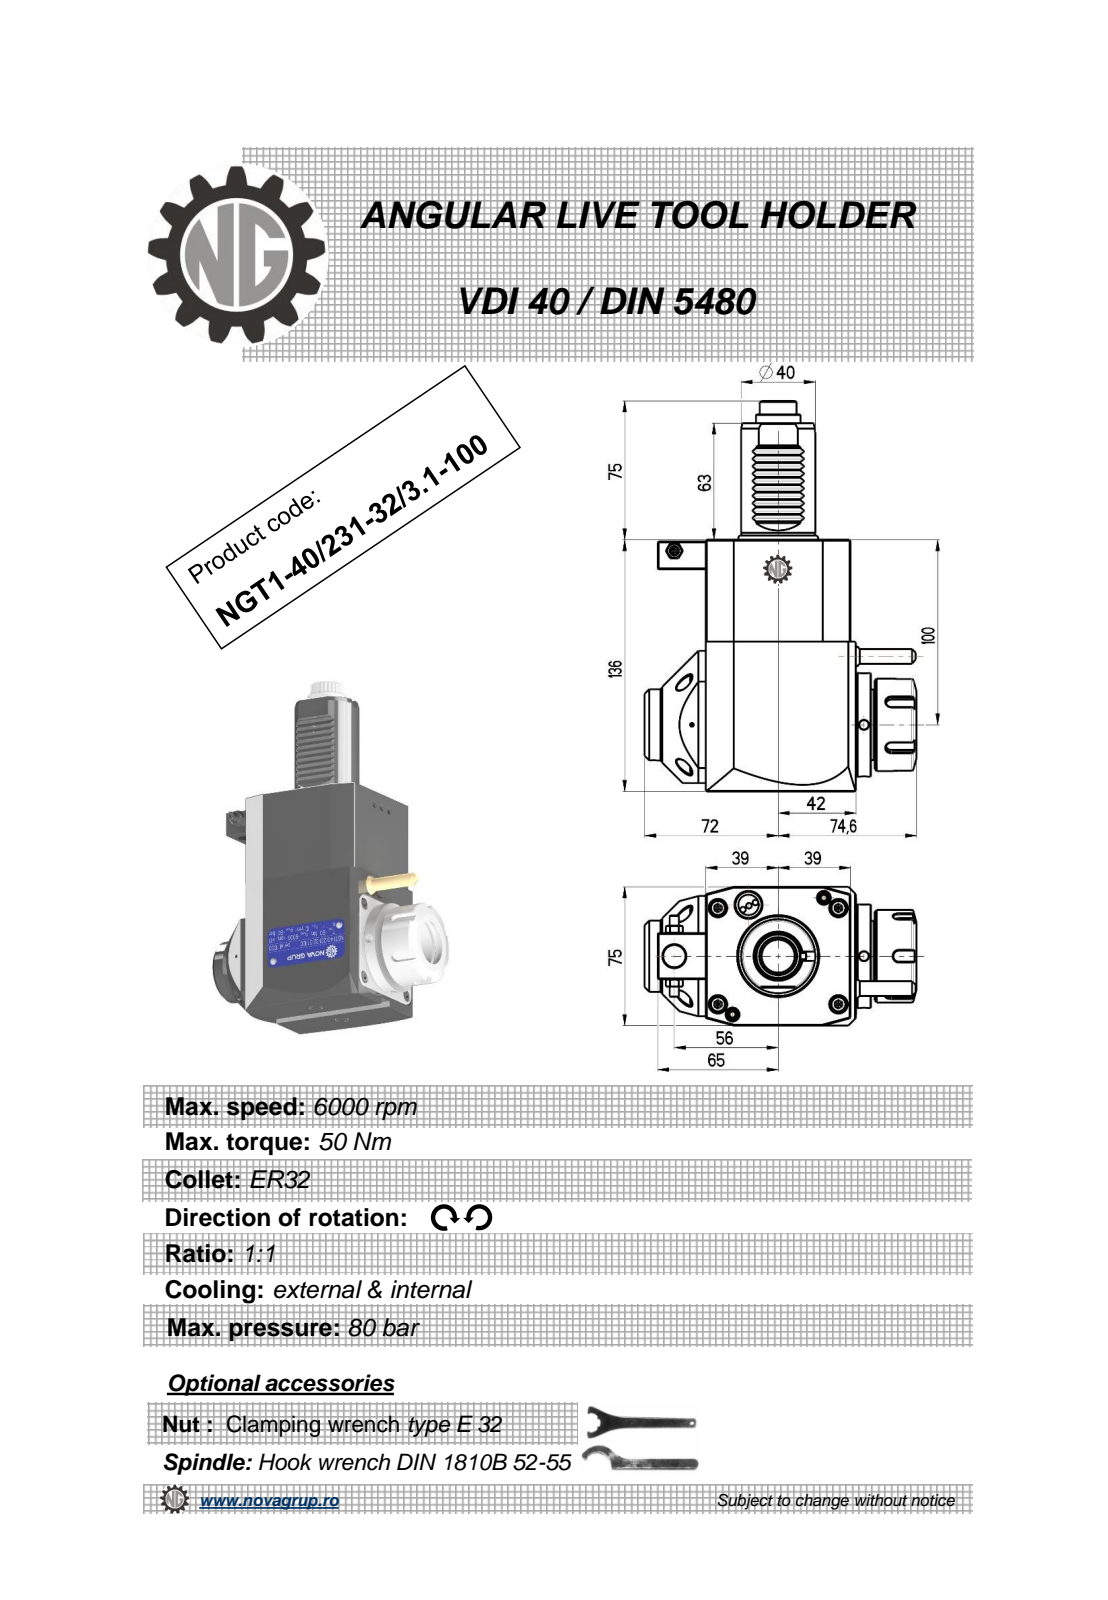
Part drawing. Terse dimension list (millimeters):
name: NGT1_40_231_32_3_1_100
written by: PRO/ENGINEER BY PARAMETRIC TECHNOLOGY CORPORATION, 2010280 (CONFIG_CONTROL_DESIGN)
unit: mm
bodies: 1 solid, 537 faces (193 planar, 183 cylindrical, 161 other)
size: 211 × 146.6 × 75
volume: 1 028 000 mm³; area: 78 944 mm²
holes: 3× ⌀5, 1× ⌀3, 1× ⌀4.2, 1× ⌀9.5, 1× ⌀12, 1× ⌀27
bosses: 1× ⌀56, 1× ⌀50, 1× ⌀43, 1× ⌀40, 1× ⌀38.5, 1× ⌀24, 1× ⌀11.2, 1× ⌀8.96
rounds: 48× R2.08, 12× R0.26, 10× R0.3, 6× R0.22, 5× R3, 1× R9.08, 1× R9.92, 1× R15
face distances: 75, 136, 78, 81, 3, 84.88, 7.5, 80.8, 2.8, 0.5
hole spacings: 40.93, 57.24, 91.5, 102.25, 138.89
